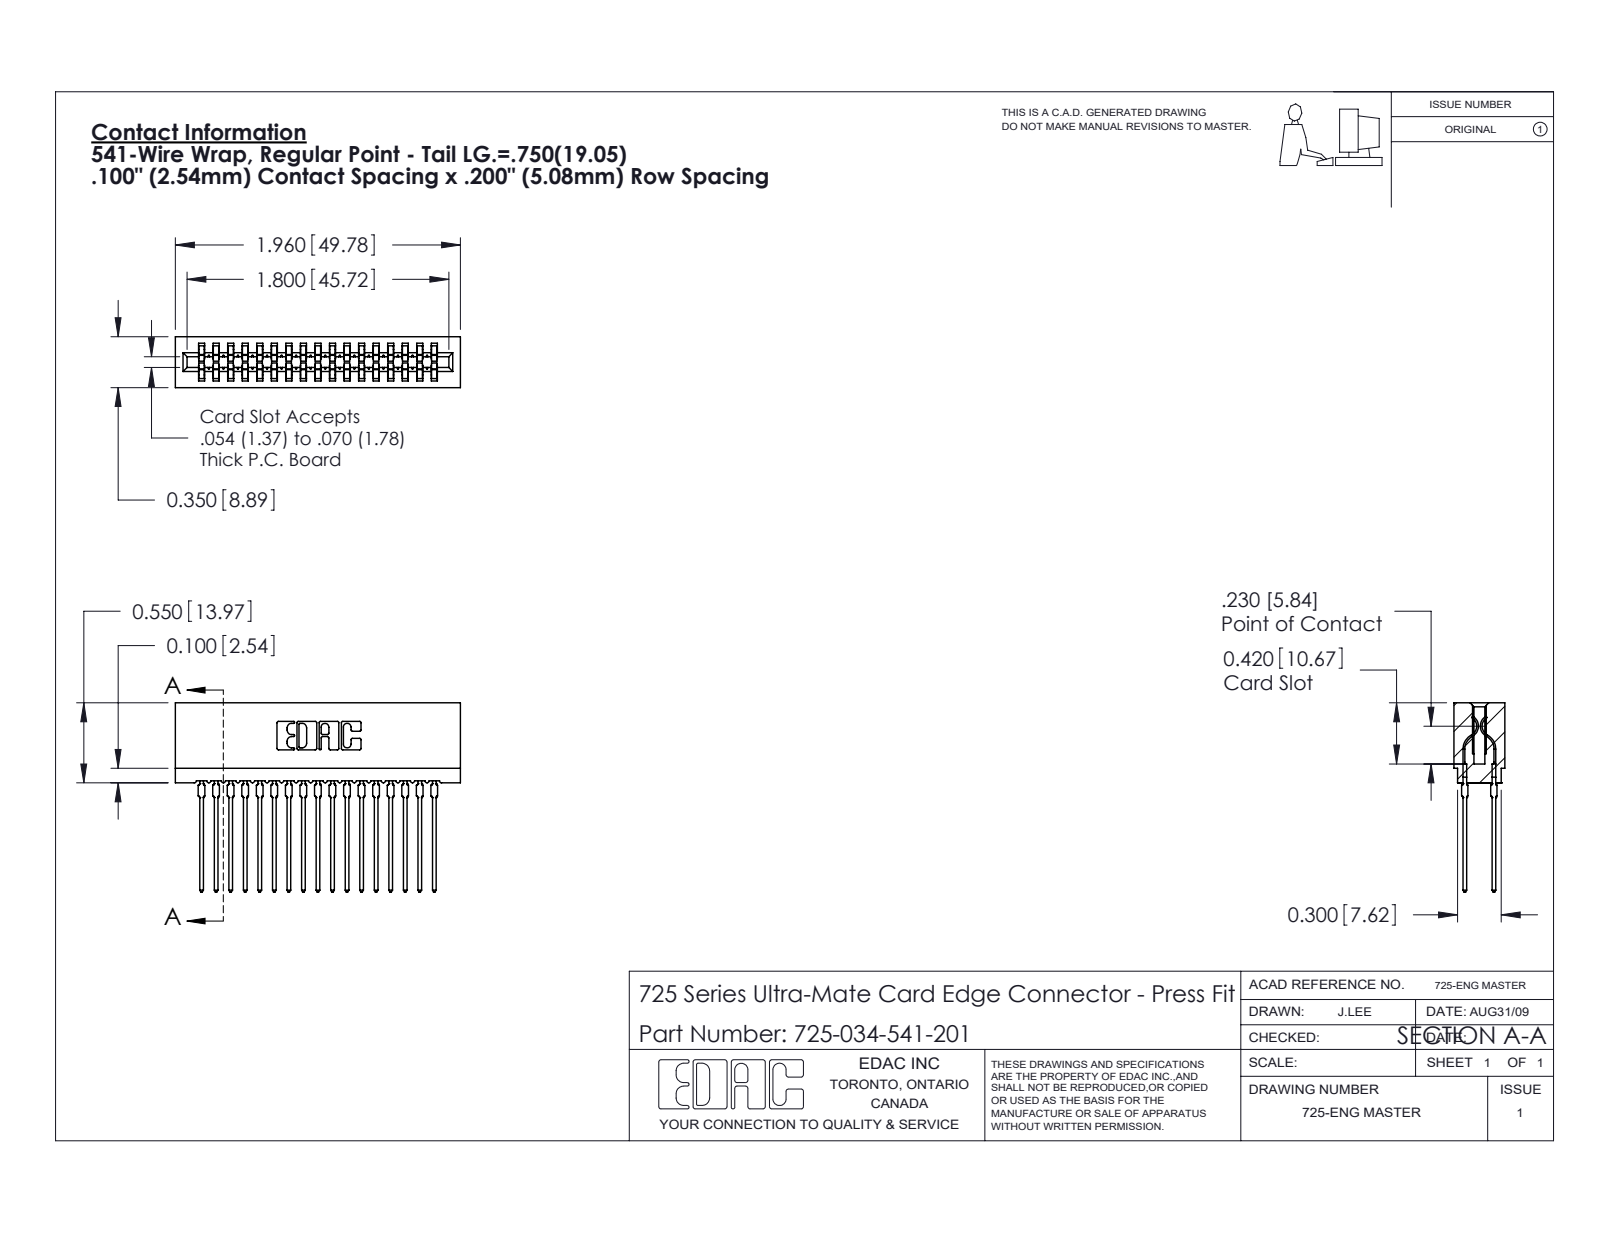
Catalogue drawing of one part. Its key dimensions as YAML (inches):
part_name: "725-034-541-201; 745-292-001_541; 725 Part_Insulator Option - 01"
step_written_by: "SolidWorks 2020 (CONFIG_CONTROL_DESIGN)"
units: inches
bodies: {solids: 35, faces: 3138, planar: 1619, cylindrical: 635, other: 884}
overall_size: [1.96, 1.301, 0.35]
volume: 0.259
surface_area: 14.1
partial_cylinders:
  - {radius: 0.021, count: 68}
  - {radius: 0.015, count: 34}
  - {radius: 0.01, count: 22}
  - {radius: 0.005, count: 8}
  - {radius: 0.011, count: 8}
  - {radius: 0.007, count: 6}
  - {radius: 0.031, count: 6}
  - {radius: 0.026, count: 3}
face_to_face_distances: [0.2, 0.1, 0.3, 0.063, 0.287, 0.4, 0.5, 0.6, 0.7, 0.35]
